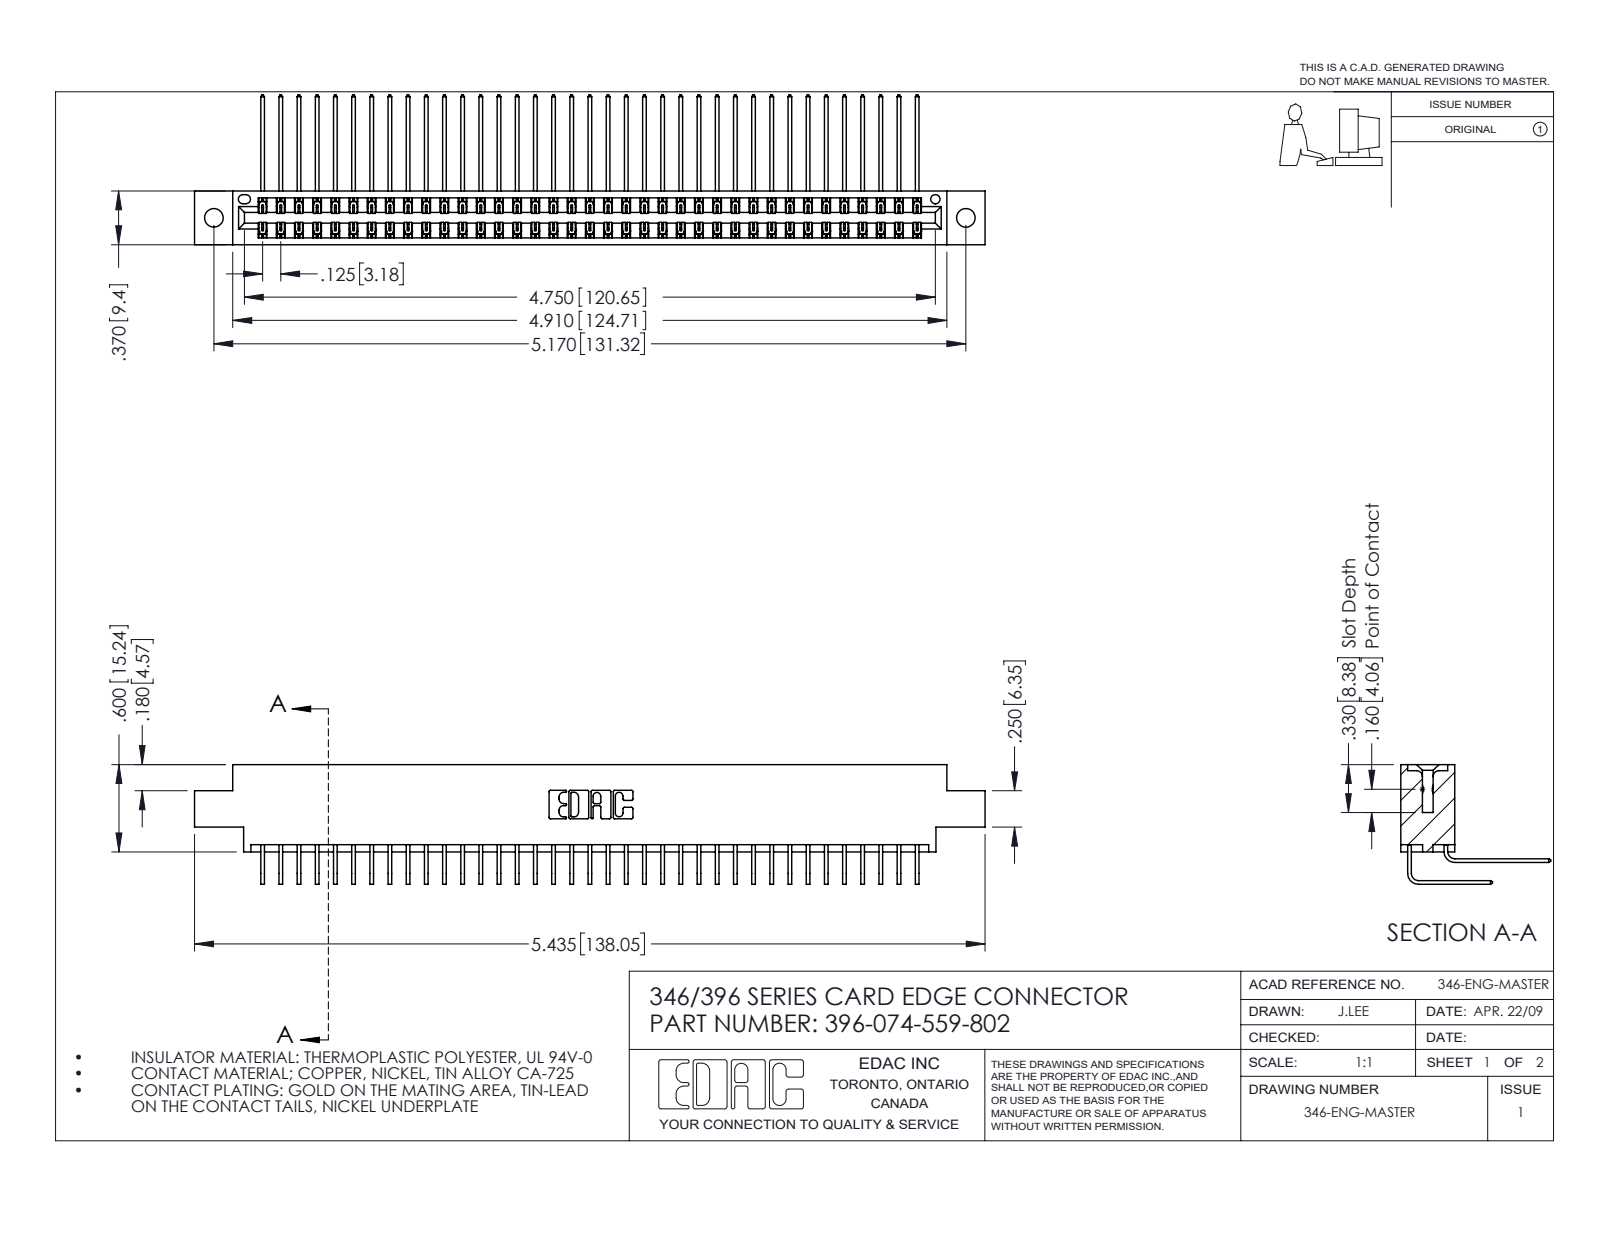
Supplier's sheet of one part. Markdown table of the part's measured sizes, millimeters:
| quantity | value |
| --- | --- |
| part name | 346 Part_0.170 Offset - 0.128 Dia; 345-292-001_559 Tail - 2; 345-292-001_558 559 Tail - 1; 396-074-559-802 |
| STEP written by | SolidWorks 2016 (CONFIG_CONTROL_DESIGN) |
| units | millimeters |
| bodies | 75 solids, 4122 faces (2818 planar, 1304 cylindrical, 0 other) |
| overall size | 138 × 26.2 × 20.9 |
| volume | 13 700 mm³ |
| surface area | 20 650 mm² |
| round holes (diameter × count) | 3.3 × 2, 1.6 × 1 |
| partial cylindrical surfaces (radius × count) | 0.2 × 111, 0.3 × 22, 0.2 × 6, 0.8 × 6, 0.7 × 3, 0.4 × 2, 0.6 × 2, 0.6 × 2 |
| main face-to-face distances | 1.2, 8.2, 0.6, 9.4, 6.4, 1.8, 7.6, 7, 3.8, 5.6 |
| hole center spacings | 6.2, 126, 131.3 |
